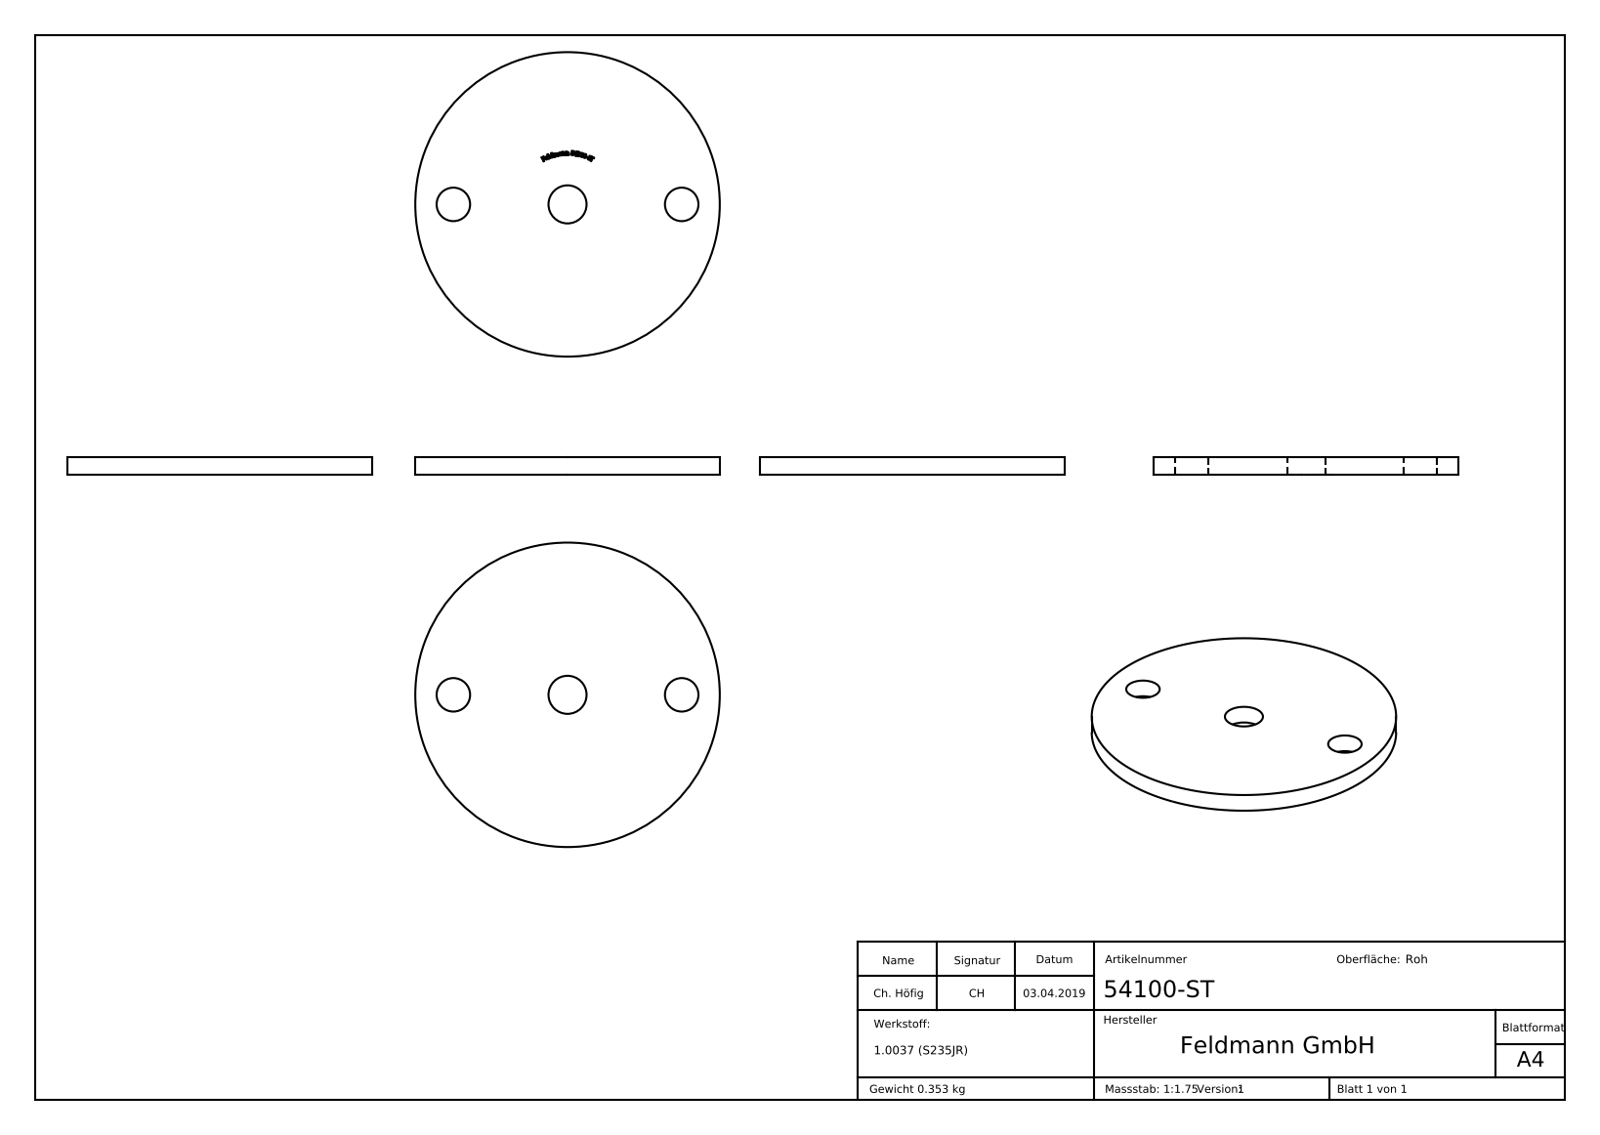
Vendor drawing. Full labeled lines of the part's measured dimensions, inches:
Part name (STEP PRODUCT): 54100-ST
STEP written by: SolidWorks 2015 (CONFIG_CONTROL_DESIGN)
Units: inches
Bodies: 1 solid, 214 faces (117 planar, 8 cylindrical, 89 other)
Overall size (bounding box): 3.937 × 3.937 × 0.236
Volume: 2.761 in³ · Surface area: 27.32 in²
Round holes (diameter × count): ⌀0.433 ×2, ⌀0.492 ×1
Round bosses / shafts (diameter × count): ⌀3.937 ×1
Main face-to-face distances: 0.236, 0.232, 0.021, 0.026, 0.026, 0.033, 0.028, 0.031, 0.052, 0.029
Hole centre spacings: 1.476, 2.953
